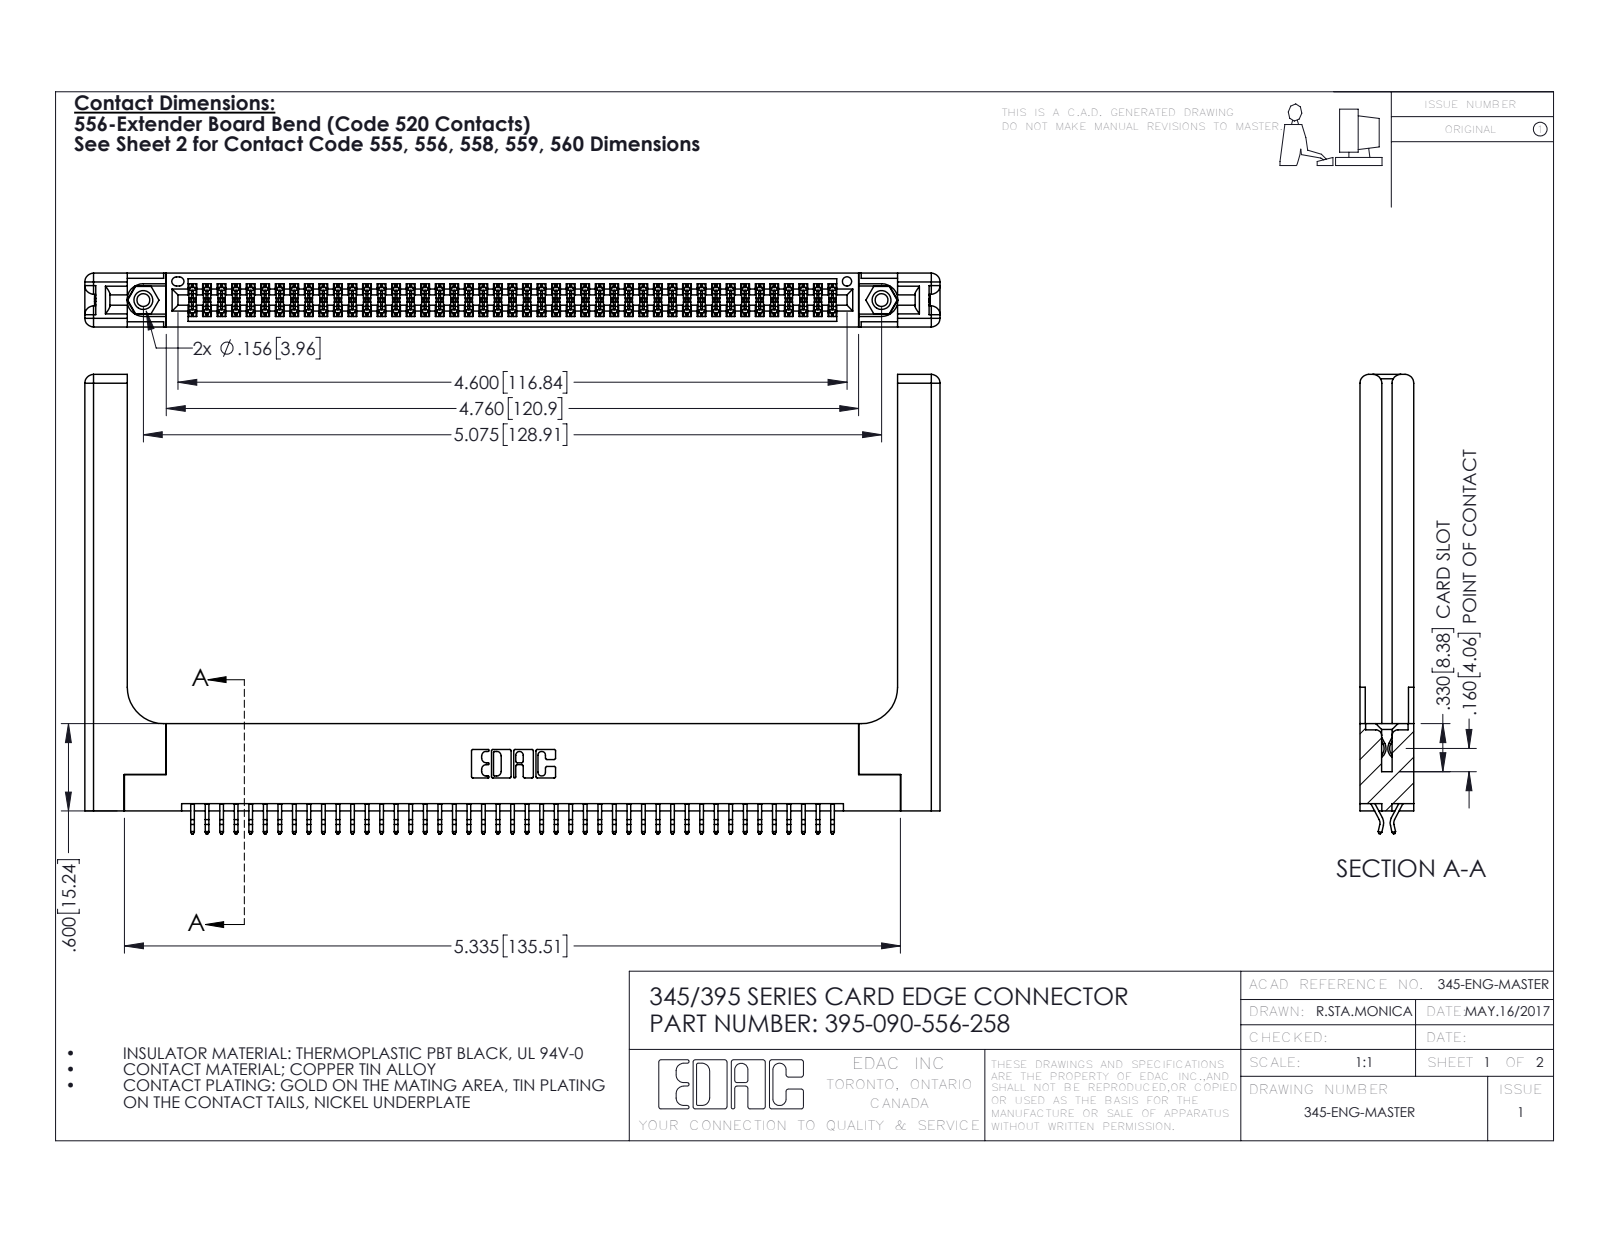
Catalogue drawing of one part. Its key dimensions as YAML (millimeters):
part_name: "345-220-058_345-220-058; 395-090-556-258; 345-250-001_345-250-001-102; 345 Part_Flush Mounting Lugs - 0.156 Dia-TH (+1 more)"
step_written_by: "SolidWorks 2016 (CONFIG_CONTROL_DESIGN)"
units: millimeters
bodies: {solids: 95, faces: 5422, planar: 3558, cylindrical: 1804, other: 60}
overall_size: [149.3, 80.2, 9.4]
volume: 23010
surface_area: 26520
round_holes:
  - {diameter: 2.3, count: 2}
  - {diameter: 3.2, count: 2}
  - {diameter: 4, count: 2}
  - {diameter: 1.6, count: 1}
round_bosses_or_shafts:
  - {diameter: 3.9, count: 2}
partial_cylinders:
  - {radius: 0.2, count: 135}
  - {radius: 0.3, count: 22}
  - {radius: 1.5, count: 16}
  - {radius: 0.2, count: 6}
  - {radius: 0.8, count: 6}
  - {radius: 0.7, count: 3}
  - {radius: 0.3, count: 2}
  - {radius: 0.4, count: 2}
face_to_face_distances: [1.8, 9.4, 7.6, 5.1, 0.6, 2.5, 6.9, 5.7, 3.8, 3.8]
hole_center_spacings: [6.9, 122.9, 128.9]
